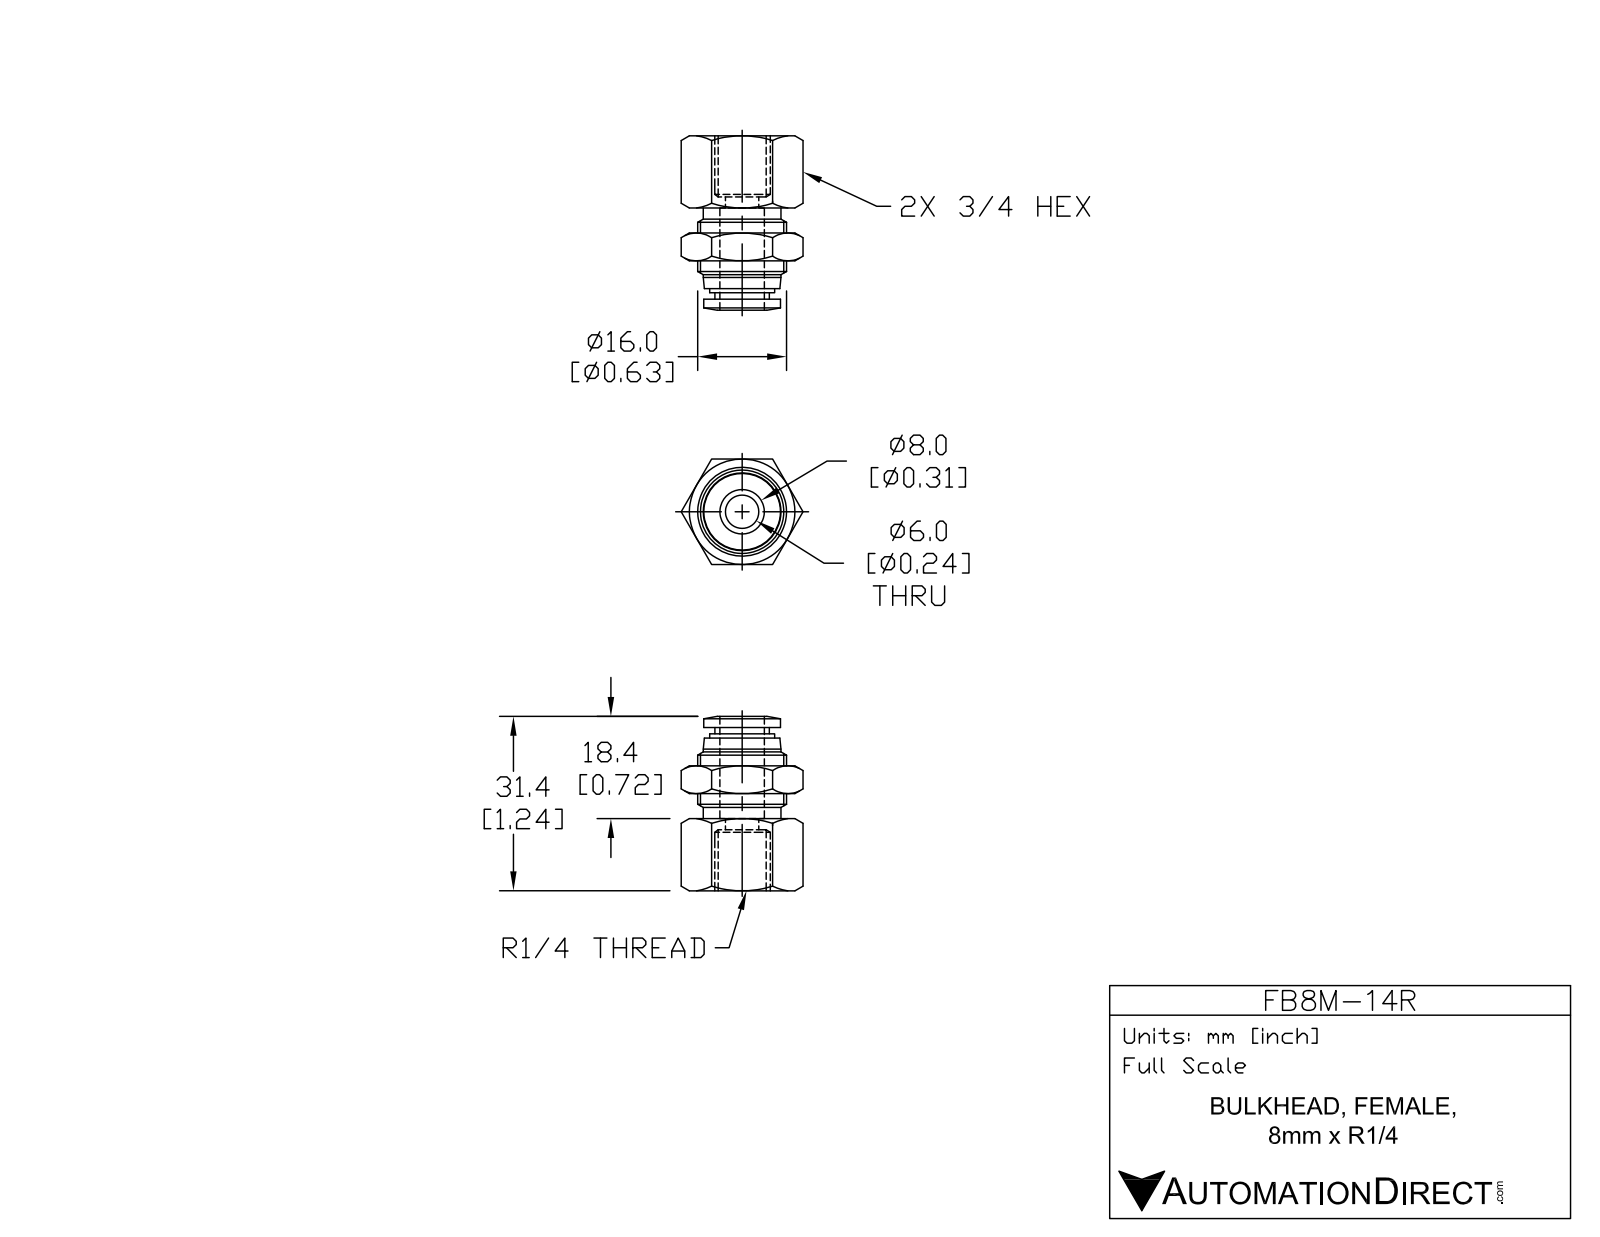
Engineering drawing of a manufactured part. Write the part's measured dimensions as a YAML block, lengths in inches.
part_name: "FB8M-14R"
step_written_by: "SolidWorks 2015 (AUTOMOTIVE_DESIGN)"
units: inches
bodies: {solids: 1, faces: 75, planar: 22, cylindrical: 18, other: 35}
overall_size: [1.236, 0.864, 0.748]
volume: 0.32
surface_area: 5.632
round_holes:
  - {diameter: 0.236, count: 1}
  - {diameter: 0.327, count: 1}
round_bosses_or_shafts:
  - {diameter: 0.63, count: 1}
  - {diameter: 0.551, count: 1}
  - {diameter: 0.543, count: 1}
  - {diameter: 0.461, count: 1}
  - {diameter: 0.386, count: 1}
face_to_face_distances: [0.748, 0.512, 0.079, 0.433, 0.677, 0.244, 0.165, 0.874, 0.441, 0.362]
